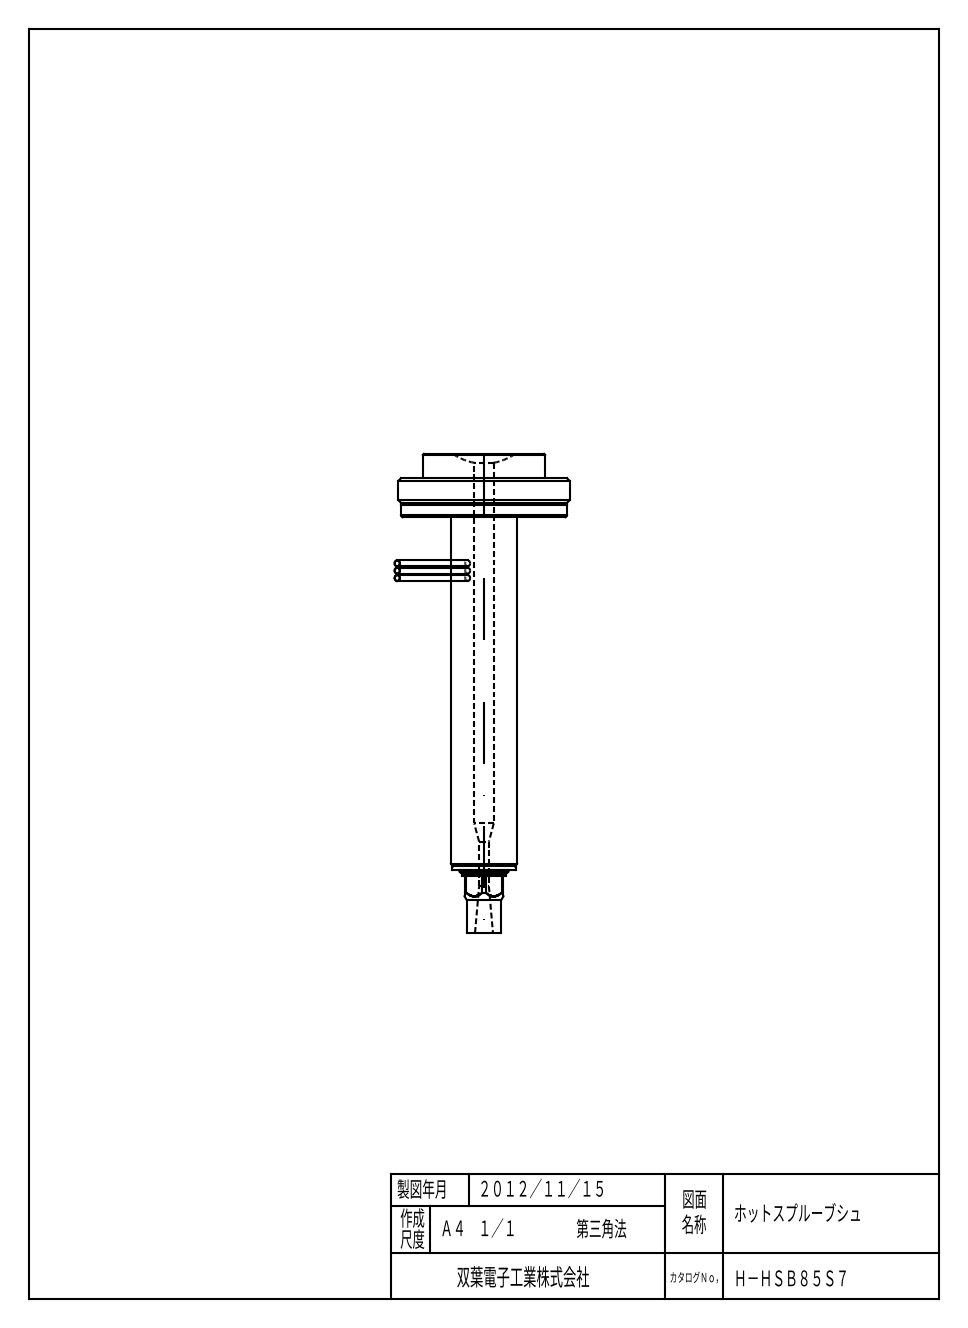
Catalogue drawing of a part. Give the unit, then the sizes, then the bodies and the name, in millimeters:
Units: millimetres
Overall size (bounding box): 160.34 × 160.34 × 98
Round holes (diameter × count): ⌀5.5 ×4, ⌀8.9 ×4, ⌀4 ×1, ⌀16 ×1
Round bosses / shafts (diameter × count): ⌀4 ×3, ⌀1.2 ×3, ⌀35 ×1, ⌀34 ×1, ⌀13.5 ×1, ⌀13 ×1, ⌀10 ×1, ⌀9.98 ×1
Partial cylindrical surfaces — rounded edges, fillets, slot ends (radius × count): R12.5 ×1
Main face-to-face distances: 5, 8, 13, 0.5, 7.5, 5.5, 3, 2.5, 72.06, 77.06
Hole centre spacings: 12.5, 17.68, 25
Volume: 19 699 mm³ · Surface area: 9 754 mm²
Bodies: 1 solid, 79 faces (23 planar, 30 cylindrical, 26 other)
Part name (STEP PRODUCT): HSB85S7
STEP written by: SIEMENS PLM Software NX 2023 (AUTOMOTIVE_DESIGN)
